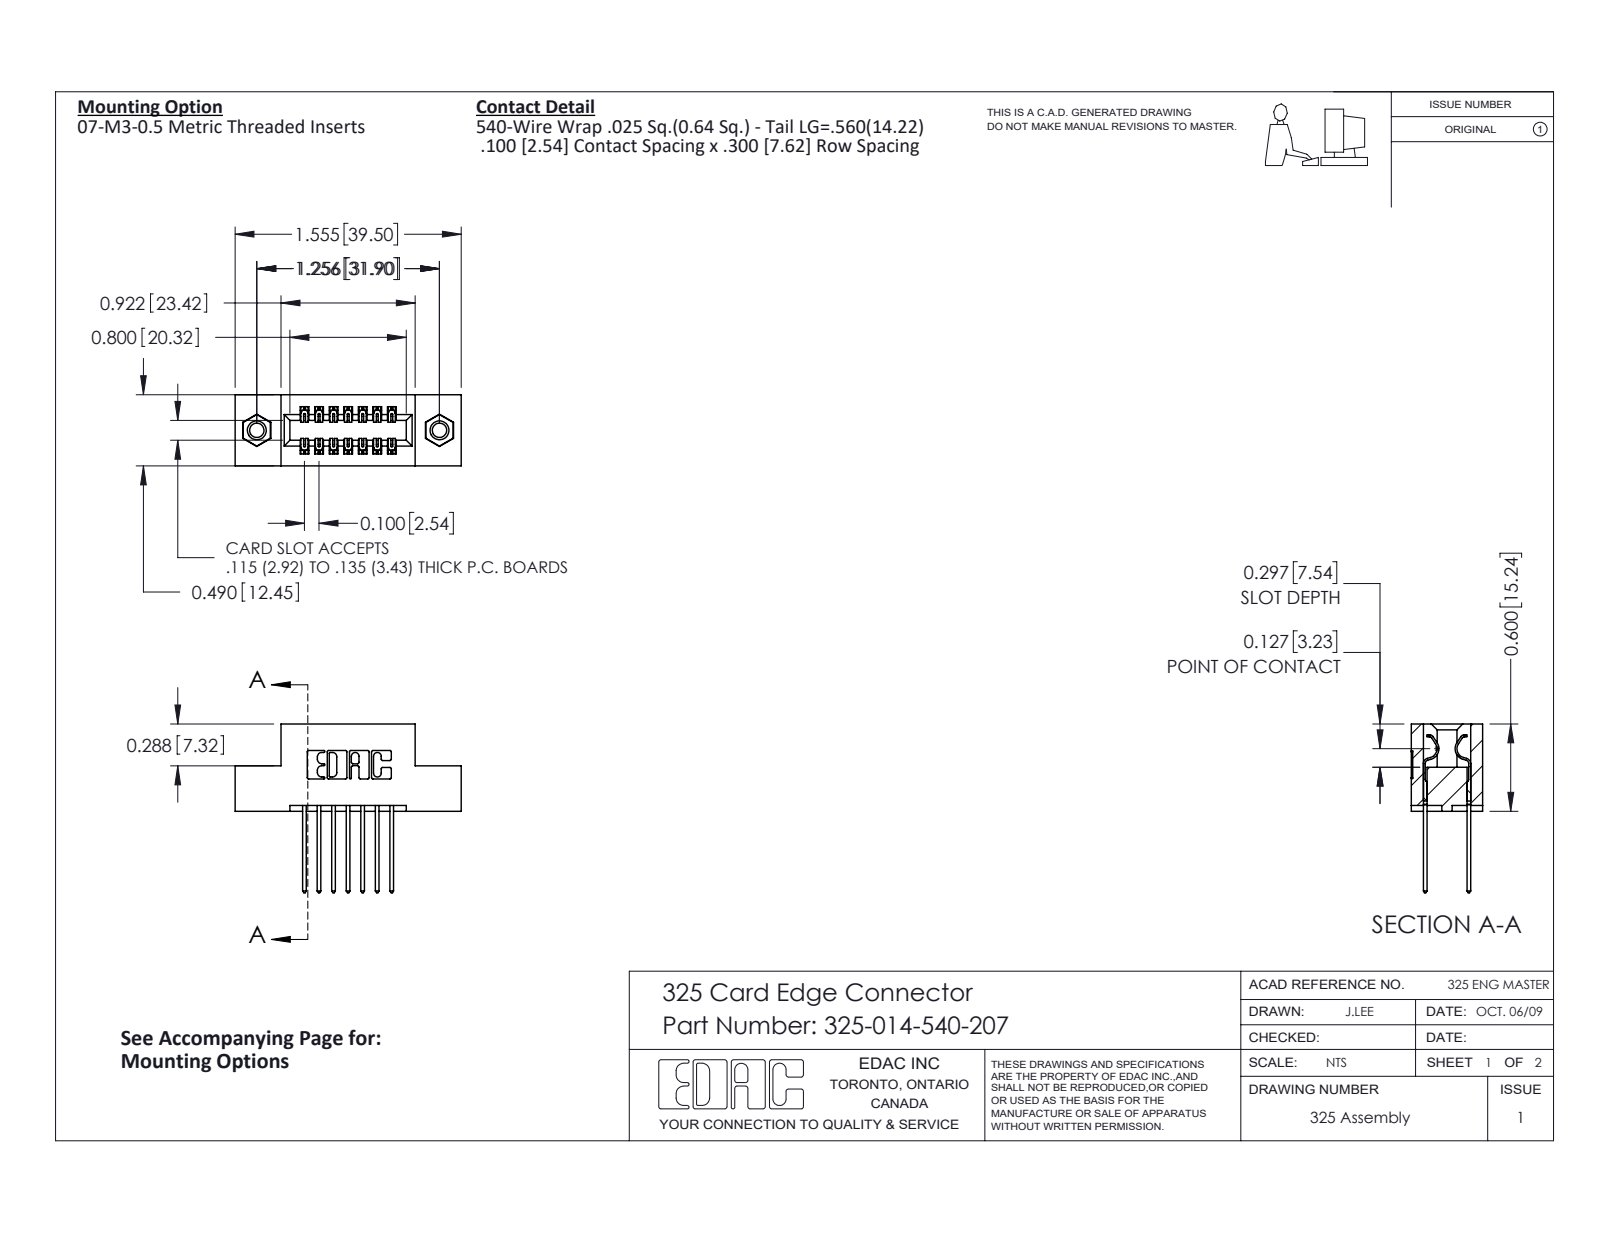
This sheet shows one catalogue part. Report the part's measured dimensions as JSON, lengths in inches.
{"part_name": "345-250-001_345-250-005-103; 325 Part_TI; 325-014-540-207; 325-292-001_325-293-140", "step_written_by": "SolidWorks 2016 (CONFIG_CONTROL_DESIGN)", "units": "inches", "bodies": {"solids": 17, "faces": 902, "planar": 606, "cylindrical": 280, "other": 16}, "overall_size": [1.555, 1.16, 0.49], "volume_in3": 0.294, "surface_area_in2": 8.197, "round_holes": [[0.098, 2], [0.125, 2], [0.16, 2]], "round_bosses_or_shafts": [[0.155, 2]], "partial_cylinders_radius": [[0.01, 22], [0.006, 21], [0.01, 14], [0.007, 6], [0.031, 6], [0.026, 3], [0.014, 2], [0.022, 2]], "face_to_face_distances": [0.3, 0.083, 0.407, 0.1, 0.2, 0.04, 0.49, 0.107, 0.383, 0.025], "hole_center_spacings": [1.256]}
